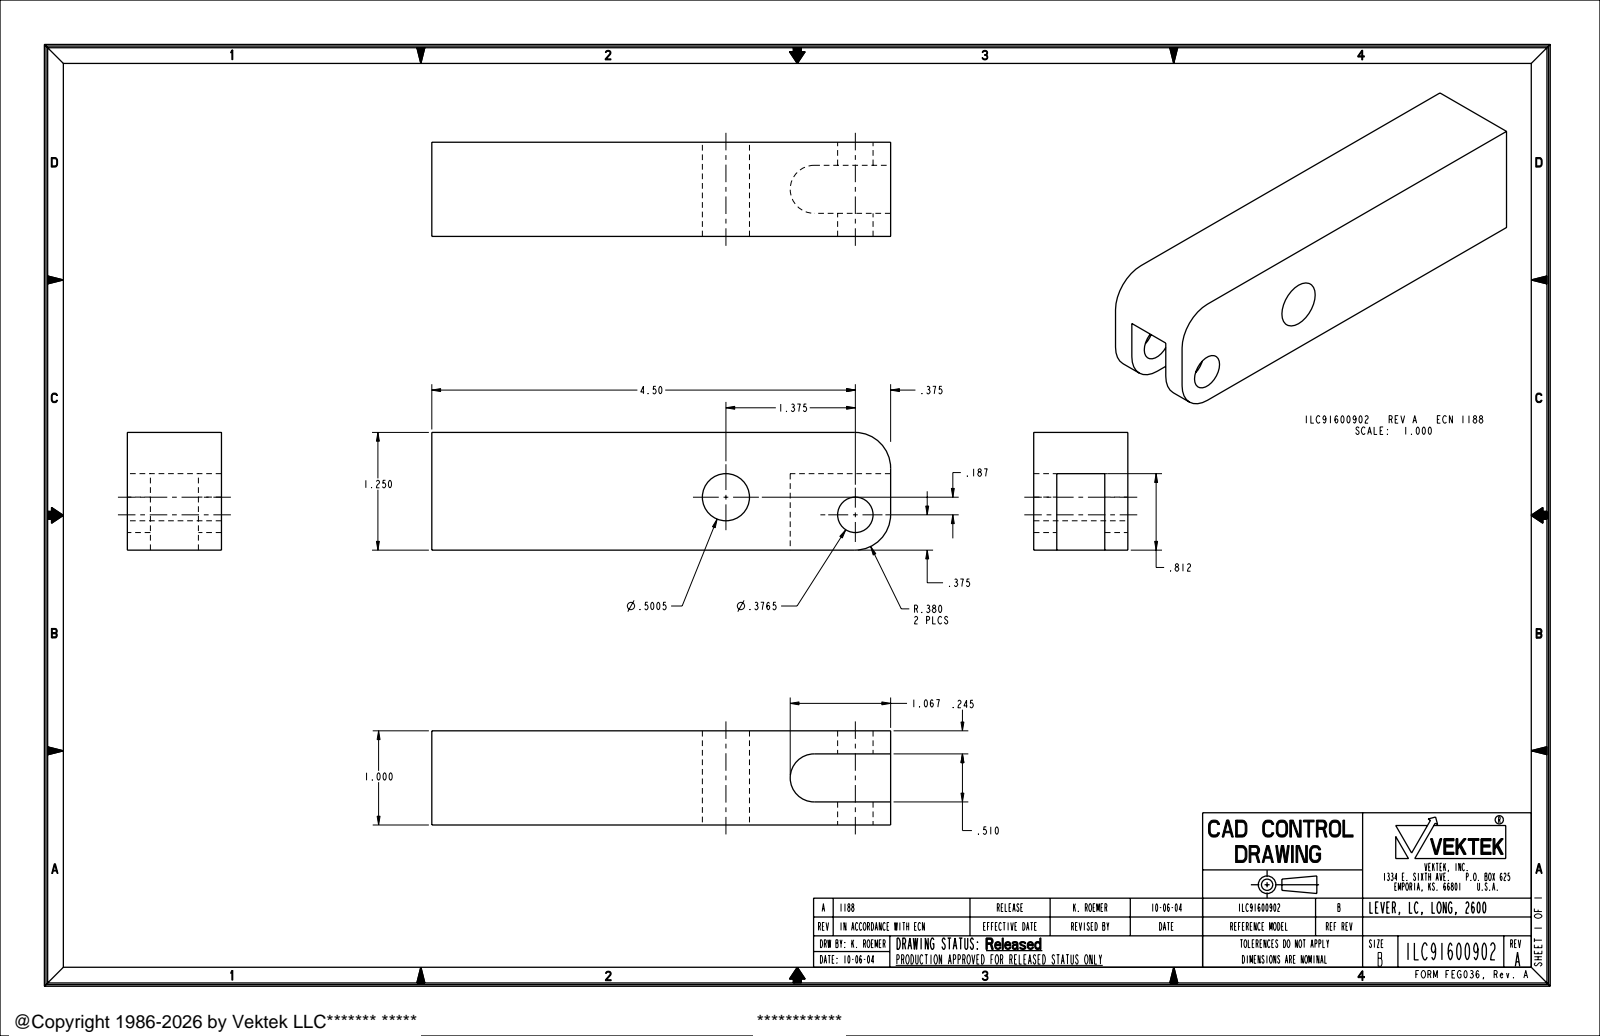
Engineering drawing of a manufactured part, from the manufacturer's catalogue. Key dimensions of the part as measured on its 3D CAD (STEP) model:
Part name (STEP PRODUCT): 91600902
STEP written by: PRO/ENGINEER BY PARAMETRIC TECHNOLOGY CORPORATION, 2004290 (CONFIG_CONTROL_DESIGN)
Units: inches
Bodies: 1 solid, 19 faces (9 planar, 10 cylindrical, 0 other)
Overall size (bounding box): 4.875 × 1.25 × 1
Volume: 5.377 in³ · Surface area: 26.88 in²
Round holes (diameter × count): ⌀0.377 ×1, ⌀0.5 ×1
Partial cylindrical surfaces — rounded edges, fillets, slot ends (radius × count): R0.38 ×2, R0.255 ×1
Main face-to-face distances: 1, 1.25, 0.245, 0.755, 0.51, 0.812, 0.438, 4.875
Hole centre spacings: 1.387
